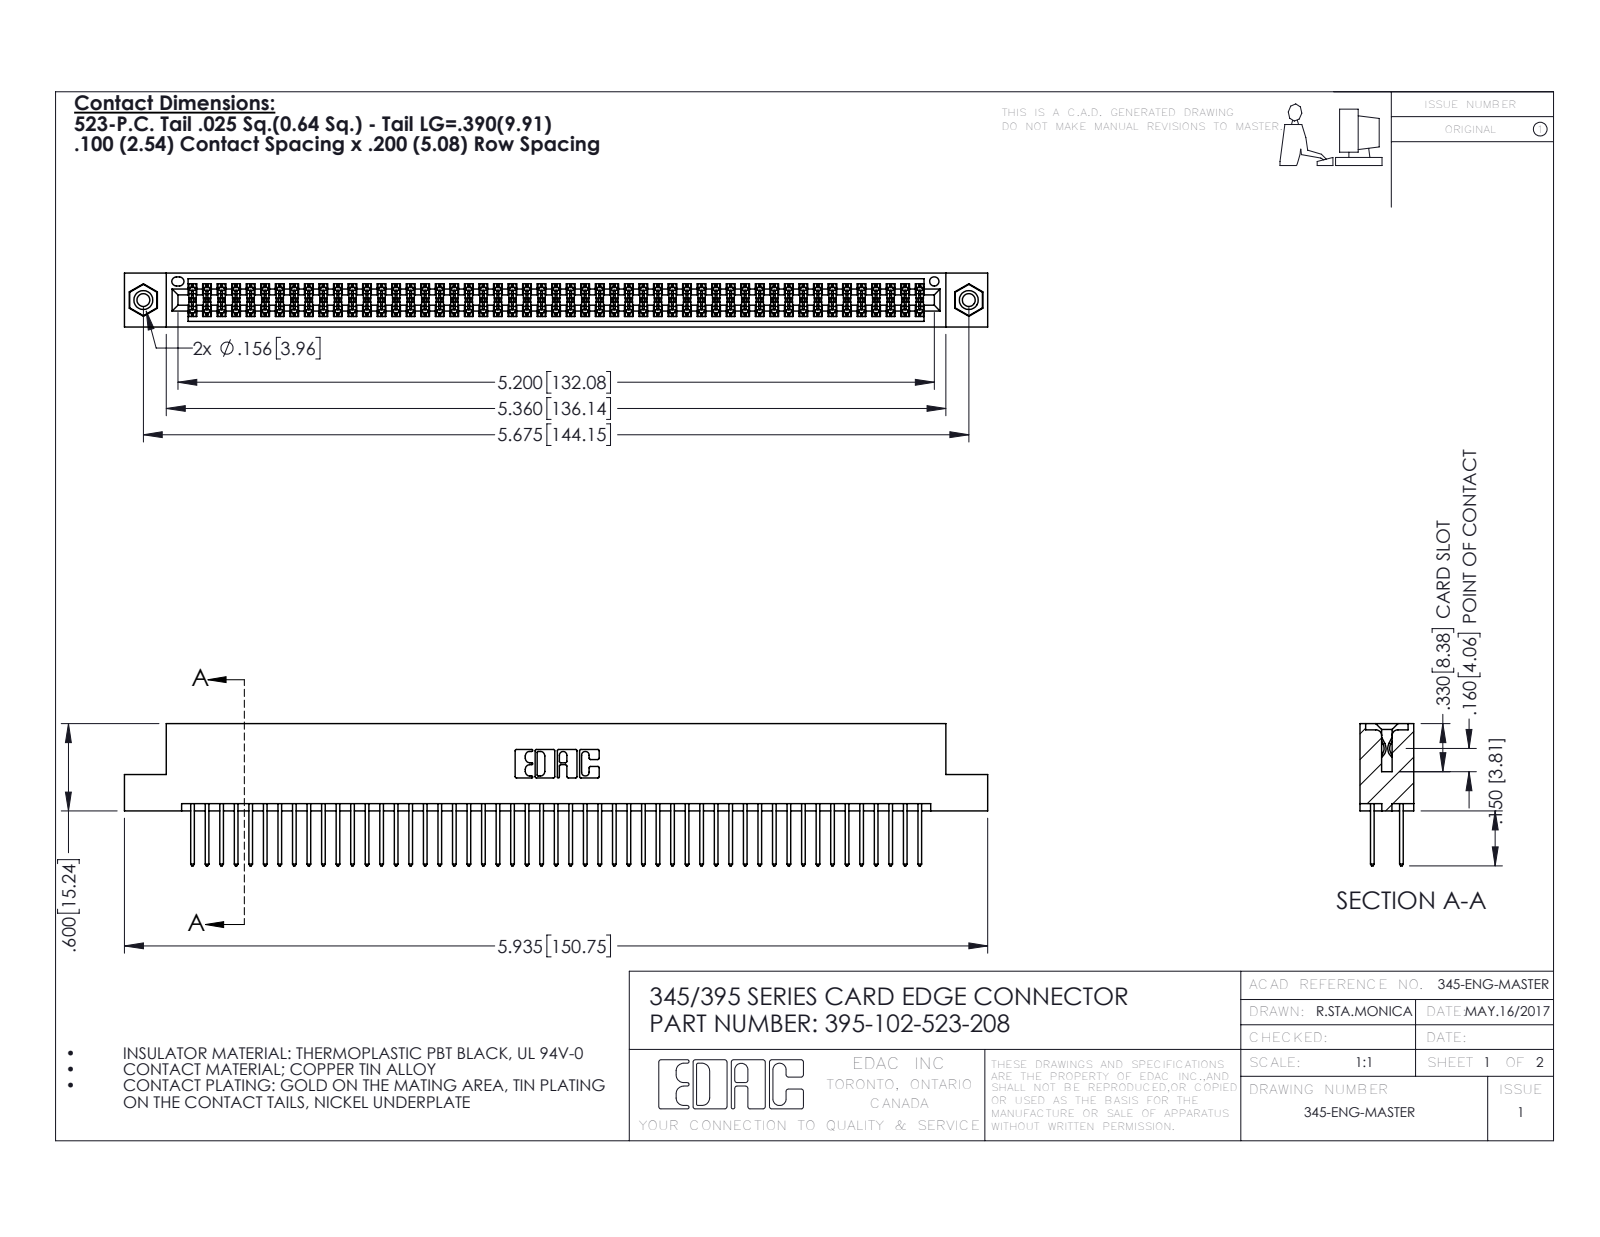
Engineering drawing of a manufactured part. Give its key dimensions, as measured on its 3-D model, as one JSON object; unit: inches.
{"part_name": "345 Part_Flush Mounting Lugs - 0.156 Dia-TI; 395-102-523-208; 345-250-001_345-250-003-102; 345-292-001_345-293-123", "step_written_by": "SolidWorks 2016 (CONFIG_CONTROL_DESIGN)", "units": "inches", "bodies": {"solids": 105, "faces": 5286, "planar": 3478, "cylindrical": 1792, "other": 16}, "overall_size": [5.935, 0.977, 0.37], "volume_in3": 0.911, "surface_area_in2": 35.95, "round_holes": [[0.089, 2], [0.125, 2], [0.156, 2], [0.064, 1]], "round_bosses_or_shafts": [[0.155, 2]], "partial_cylinders_radius": [[0.006, 153], [0.01, 102], [0.01, 22], [0.007, 6], [0.031, 6], [0.026, 3], [0.014, 2], [0.019, 2]], "face_to_face_distances": [0.072, 0.298, 0.2, 0.098, 0.272, 0.025, 0.37, 0.225, 0.175, 0.149], "hole_center_spacings": [0.27, 5.439, 5.675]}
